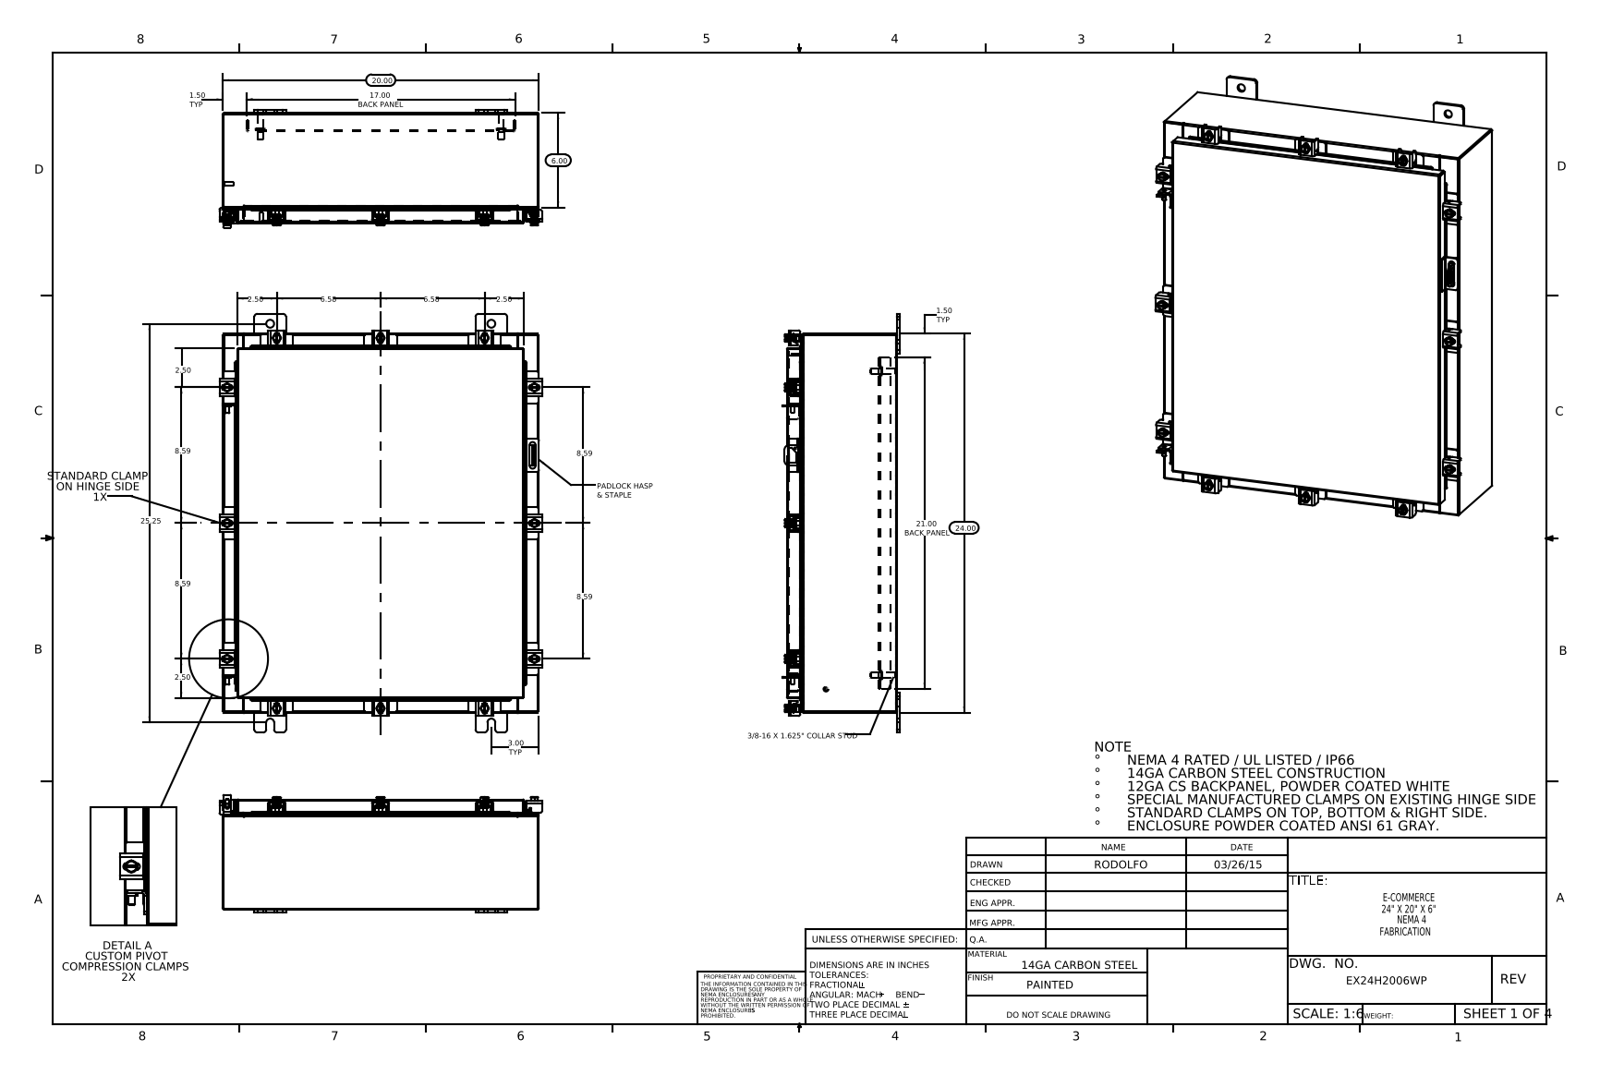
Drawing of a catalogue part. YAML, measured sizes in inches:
part_name: "EX24H2006WP Body; EX24H2006WP Cover; HW-CLN-NH-20330; EX24H2006WP Padlock Staple (+8 more)"
step_written_by: "SolidWorks 2014 (CONFIG_CONTROL_DESIGN)"
units: inches
bodies: {solids: 81, faces: 2018, planar: 1075, cylindrical: 783, other: 160}
overall_size: [26.5, 20.421, 7.453]
volume: 174.1
surface_area: 4334
round_holes:
  - {diameter: 0.213, count: 12}
  - {diameter: 0.26, count: 12}
  - {diameter: 0.5, count: 8}
  - {diameter: 0.125, count: 1}
  - {diameter: 0.25, count: 1}
round_bosses_or_shafts:
  - {diameter: 0.5, count: 12}
  - {diameter: 0.25, count: 12}
  - {diameter: 0.399, count: 10}
  - {diameter: 0.625, count: 4}
  - {diameter: 0.375, count: 4}
  - {diameter: 0.33, count: 4}
  - {diameter: 0.315, count: 2}
  - {diameter: 0.236, count: 2}
partial_cylinders:
  - {radius: 0.06, count: 54}
  - {radius: 0.013, count: 24}
  - {radius: 0.141, count: 24}
  - {radius: 0.19, count: 24}
  - {radius: 0.088, count: 22}
  - {radius: 0.12, count: 22}
  - {radius: 0.09, count: 18}
  - {radius: 0.05, count: 17}
face_to_face_distances: [0.075, 6.9, 6.975, 6.826, 0.104, 1, 1.075, 5.826, 5.9, 1.179]
hole_center_spacings: [2.347, 4.44, 8.594, 12.141, 16.602, 18.34, 20.082, 20.562]
